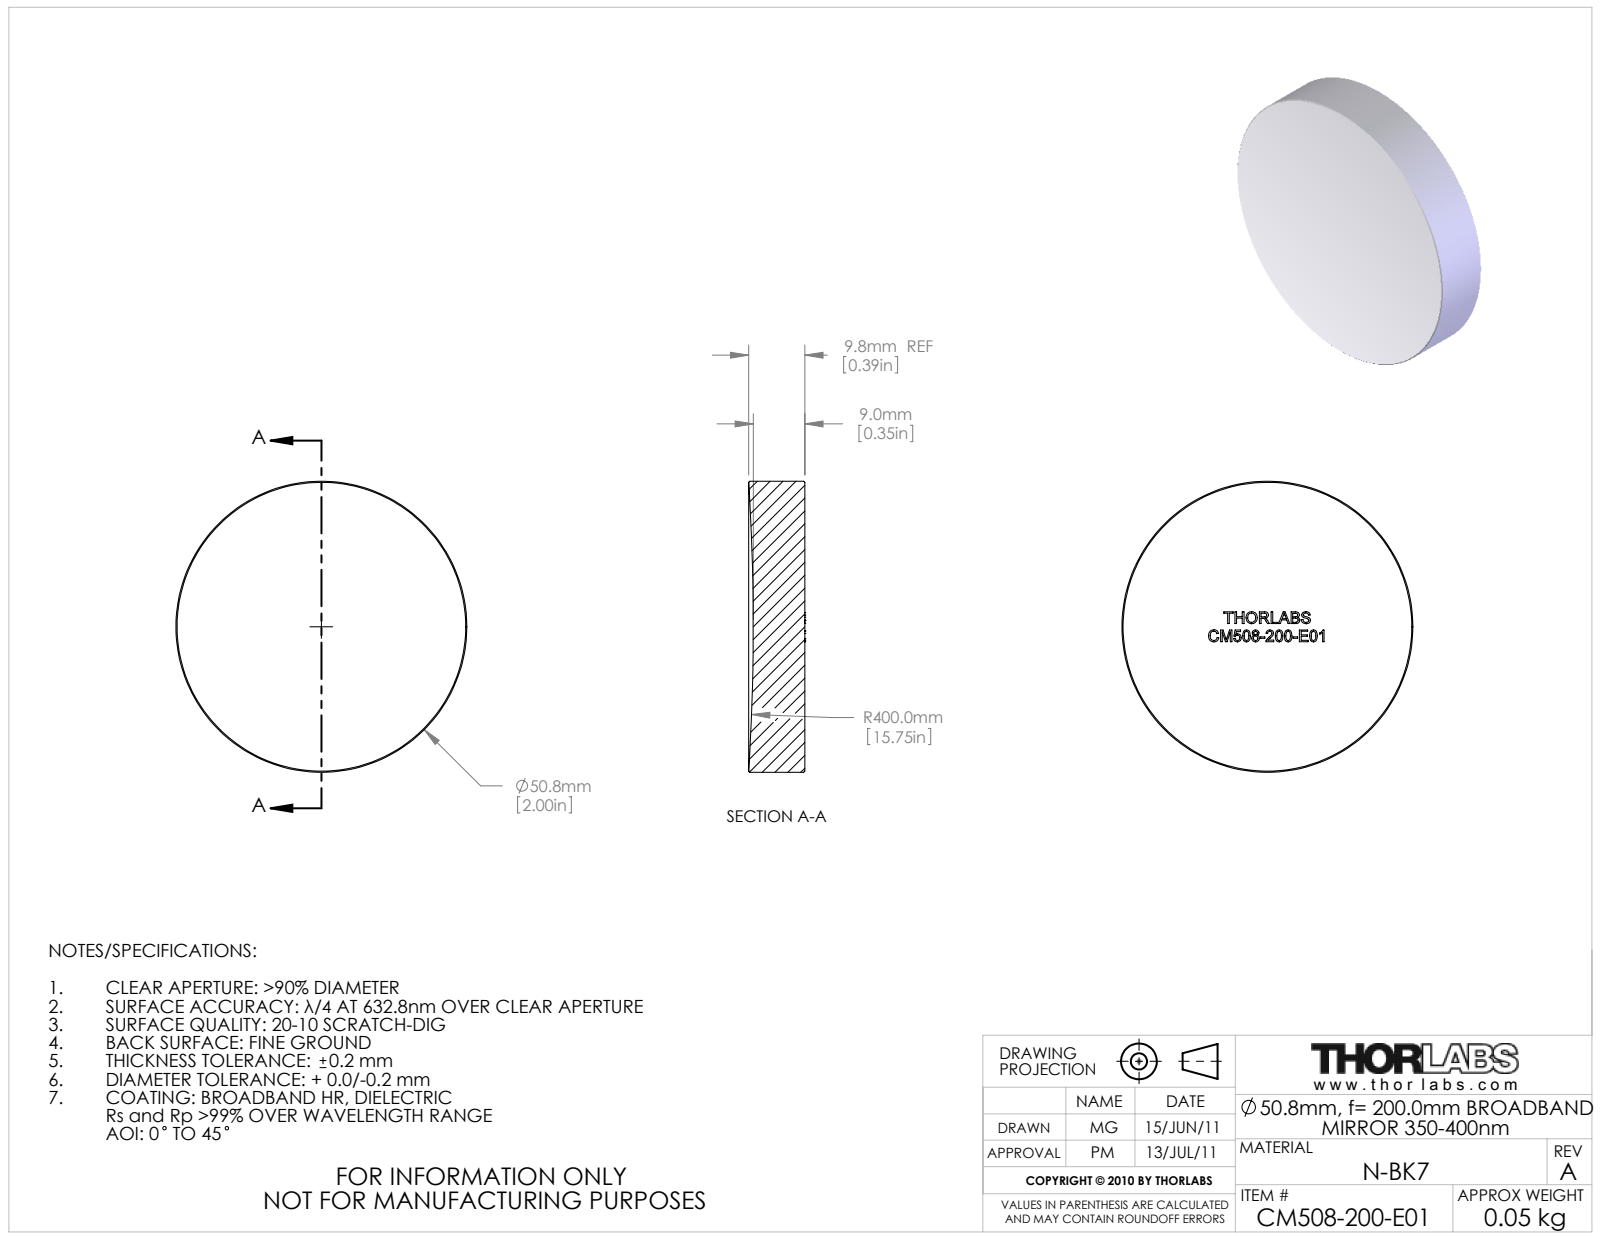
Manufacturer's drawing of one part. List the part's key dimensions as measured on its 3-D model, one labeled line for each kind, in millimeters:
Part name (STEP PRODUCT): 22618-E0W
STEP written by: SolidWorks 2011 (AUTOMOTIVE_DESIGN)
Units: millimetres
Bodies: 0 solids, 43 faces (33 planar, 2 cylindrical, 8 other)
Overall size (bounding box): 50.8 × 50.8 × 9.79
Round bosses / shafts (diameter × count): ⌀50.8 ×1
